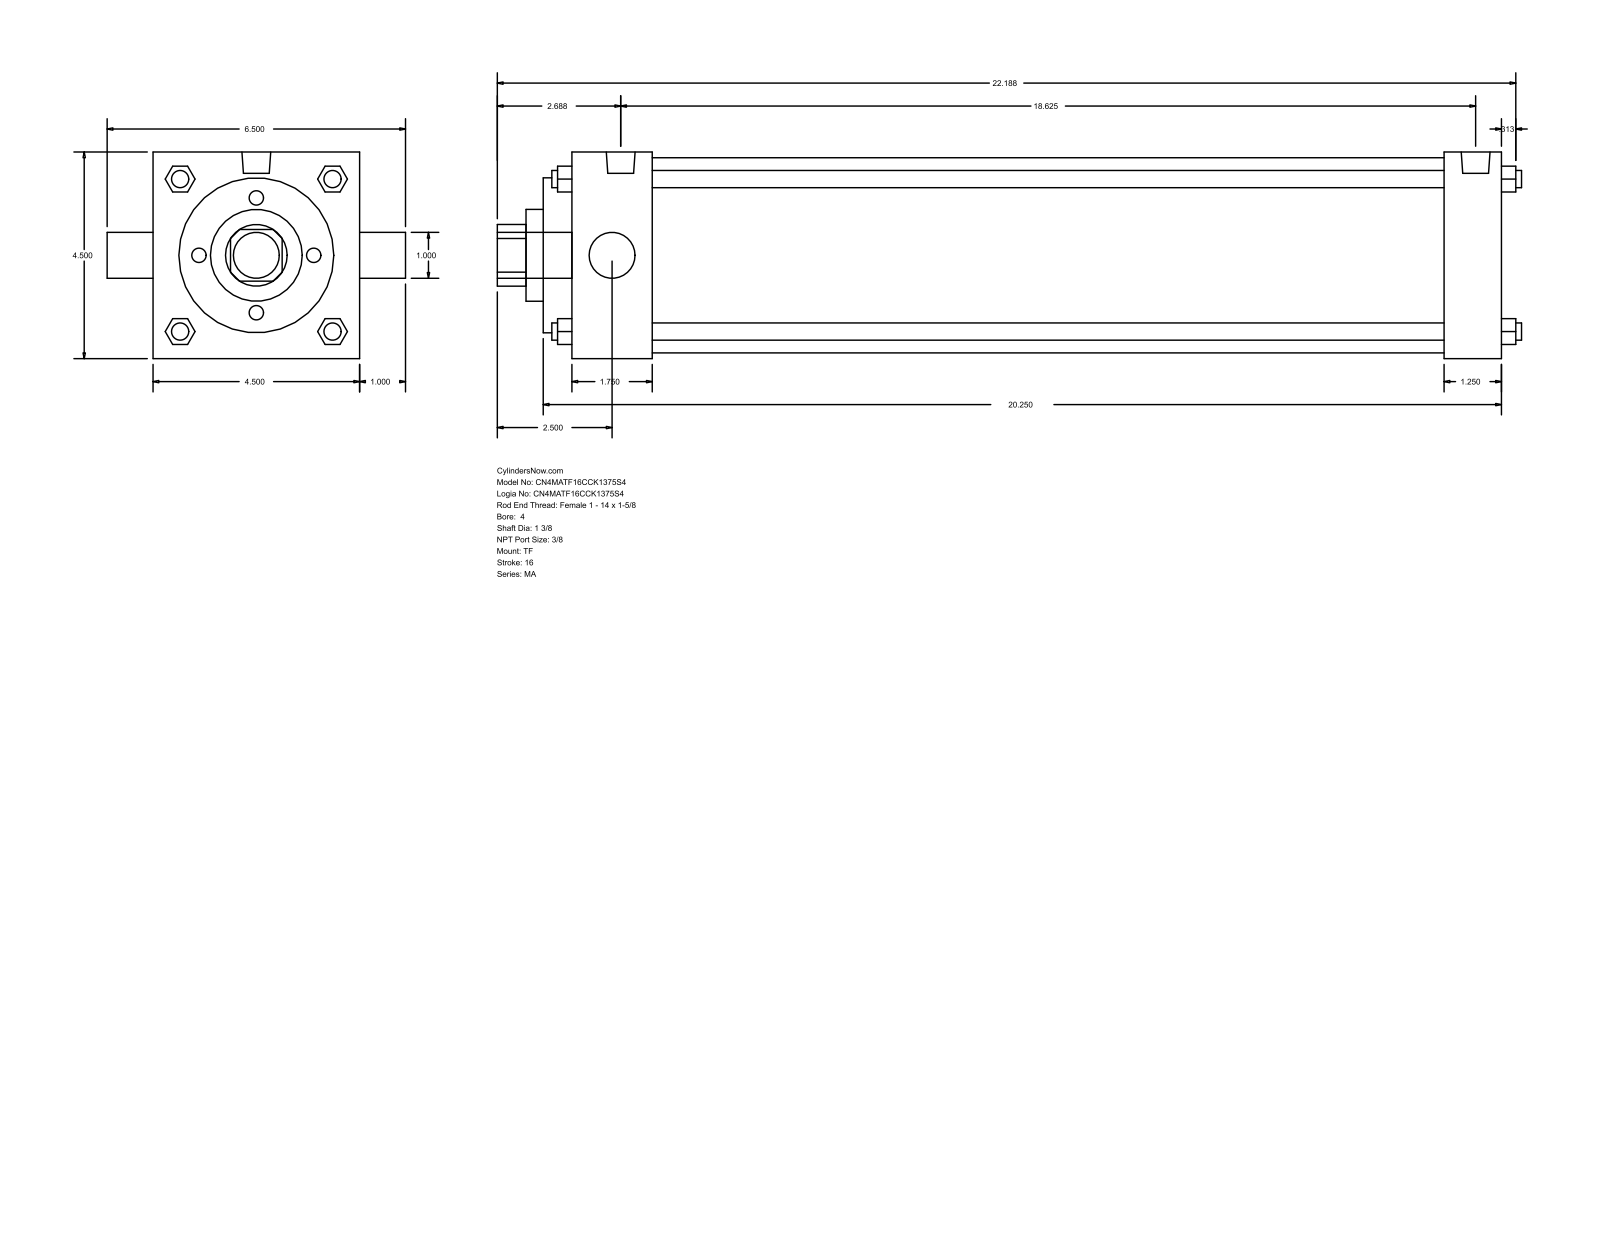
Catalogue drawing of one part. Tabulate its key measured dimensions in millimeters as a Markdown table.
| quantity | value |
| --- | --- |
| part name | MA_TF__0400_1.375 |
| STEP written by | GSSL Pune (CONFIG_CONTROL_DESIGN) |
| units | millimeters |
| bodies | 0 solids, 122 faces (93 planar, 29 cylindrical, 0 other) |
| overall size | 566.74 × 165.1 × 114.3 |
| round holes (diameter × count) | 25.4 × 1, 34.92 × 1, 50.8 × 1, 85.72 × 1, 107.95 × 1 |
| round bosses / shafts (diameter × count) | 9.53 × 4, 11.11 × 3, 15.93 × 2, 25.4 × 1 |
| partial cylindrical surfaces (radius × count) | 17.06 × 1 |
| main face-to-face distances | 114.3, 514.35, 530.22, 15.87, 498.48, 482.61, 31.74, 60.32, 44.45, 438.16 |
